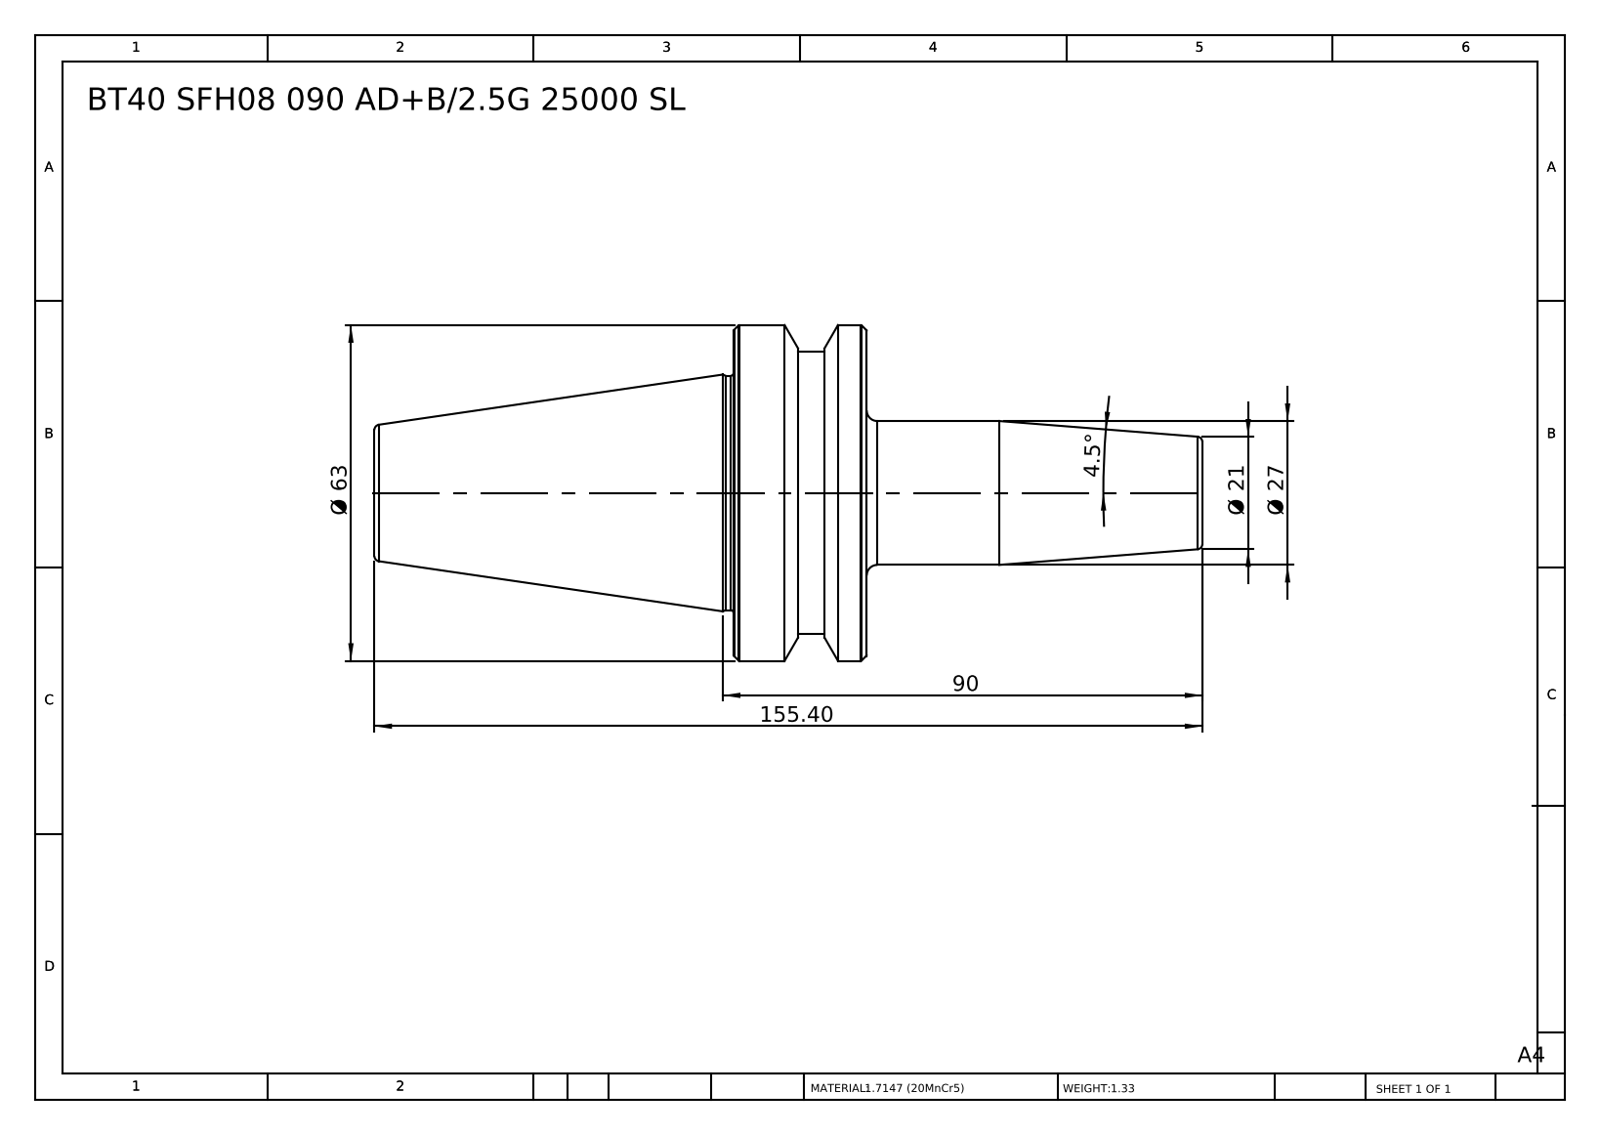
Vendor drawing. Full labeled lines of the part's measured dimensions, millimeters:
Part name (STEP PRODUCT): BT40 SFH06 090 AD+B-2.5G 25000 SL
STEP written by: SolidWorks 2014 (CONFIG_CONTROL_DESIGN)
Units: millimetres
Bodies: 1 solid, 46 faces (6 planar, 10 cylindrical, 30 other)
Overall size (bounding box): 155.4 × 63 × 63
Volume: 169 986 mm³ · Surface area: 22 993 mm²
Round bosses / shafts (diameter × count): ⌀63 ×1, ⌀53 ×1, ⌀44 ×1, ⌀27 ×1
Main face-to-face distances: 25, 92.4, 67.4, 63, 88, 155.4, 70.9, 7.9, 17.1, 84.5
